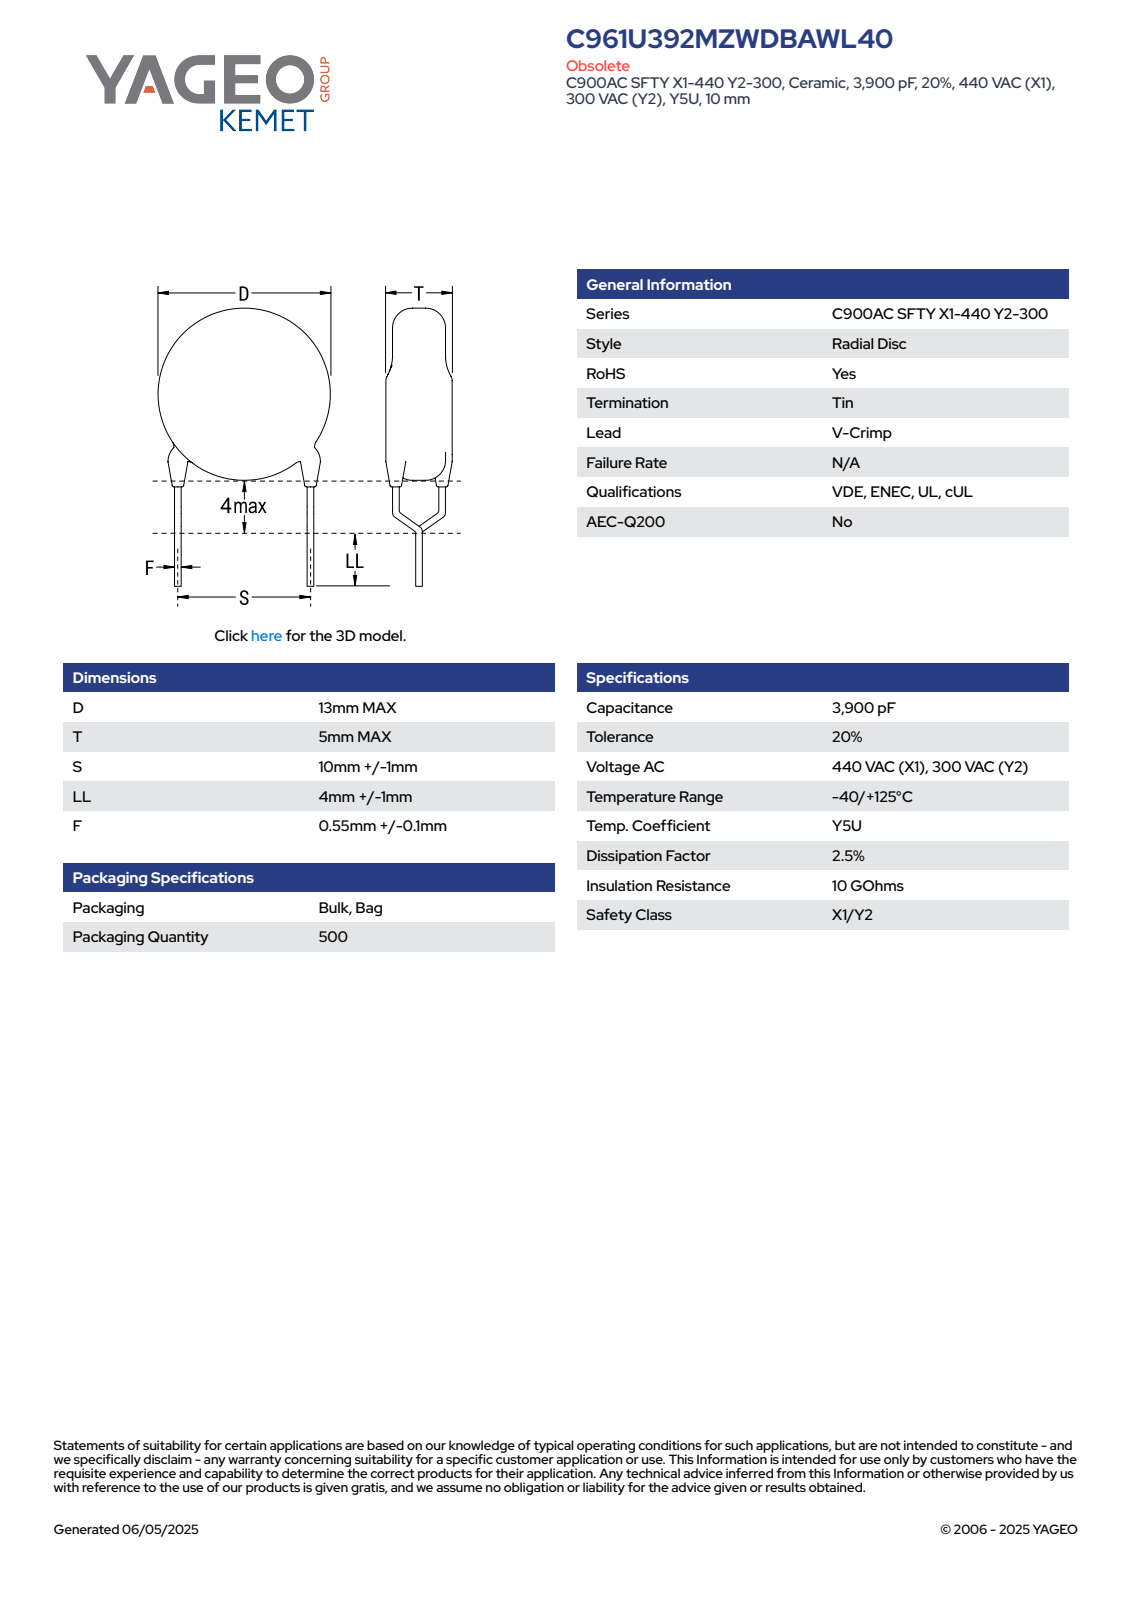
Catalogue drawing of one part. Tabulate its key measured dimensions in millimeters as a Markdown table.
| quantity | value |
| --- | --- |
| part name | CCD_VCC900_D13T5S10LL5F0.65 |
| STEP written by | SolidWorks 2014 (AUTOMOTIVE_DESIGN) |
| units | millimeters |
| bodies | 5 solids, 93 faces (65 planar, 16 cylindrical, 12 other) |
| overall size | 21.8 × 13 × 5 |
| volume | 656 mm³ |
| surface area | 500 mm² |
| round bosses / shafts (diameter × count) | 0.65 × 6, 13 × 1 |
| main face-to-face distances | 5, 7.9, 16.14, 8.24, 14.45, 6.55, 1.69, 0.46, 6.9, 0.63 |
